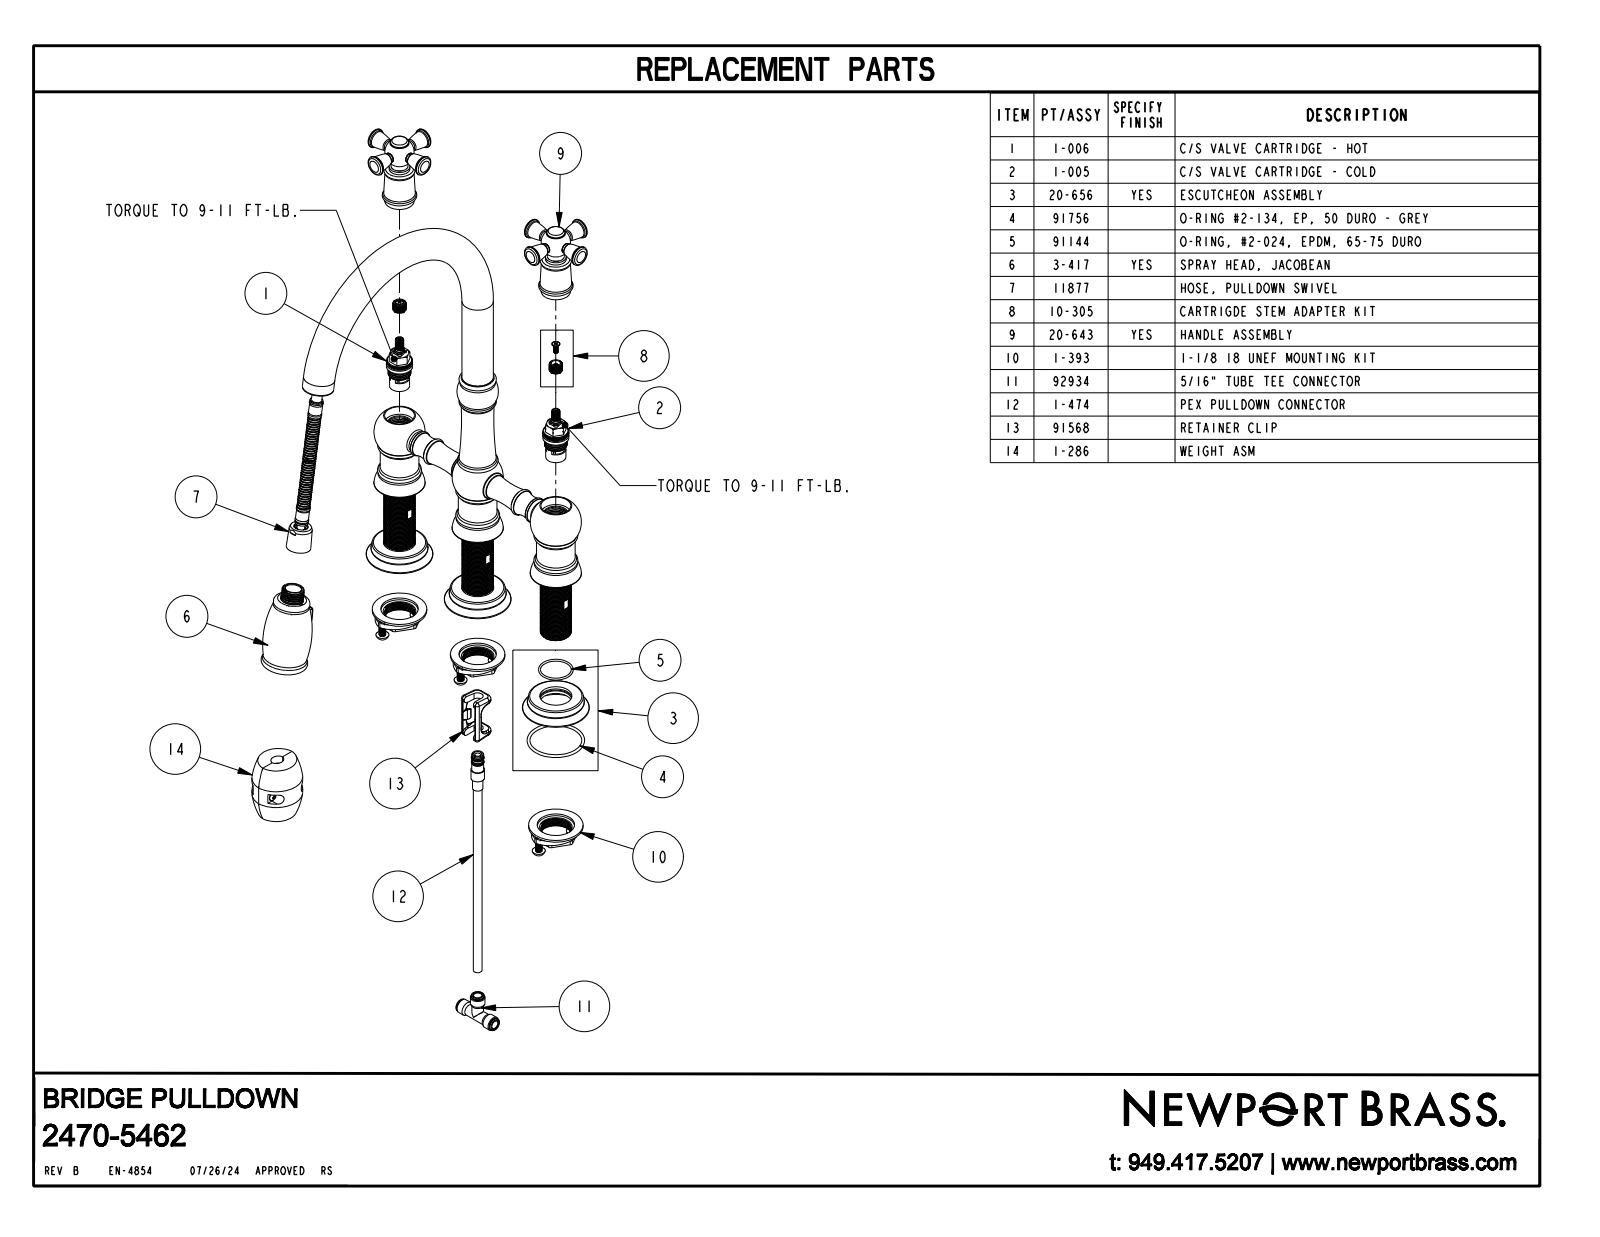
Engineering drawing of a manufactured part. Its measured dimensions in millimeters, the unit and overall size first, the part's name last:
Units: millimetres
Overall size (bounding box): 387.7 × 273 × 271.7
Round bosses / shafts (diameter × count): ⌀35.6 ×3, ⌀18.3 ×3, ⌀9.1 ×3, ⌀19.1 ×2, ⌀16.5 ×2, ⌀15.6 ×2, ⌀13 ×2, ⌀29 ×1
Partial cylindrical surfaces — rounded edges, fillets, slot ends (radius × count): R1.5 ×4, R2 ×4, R2.5 ×2, R3 ×2, R2.7 ×1
Main face-to-face distances: 14, 121.5, 107.6, 124.1, 110.1, 2.5, 70, 69.9, 124.6, 110.6
Volume: 961 600 mm³ · Surface area: 135 800 mm²
Bodies: 1 solid, 567 faces (69 planar, 71 cylindrical, 427 other)
Part name (STEP PRODUCT): 2470-5462_SW0001
STEP written by: CREO PARAMETRIC BY PTC INC, 2018400 (CONFIG_CONTROL_DESIGN)
